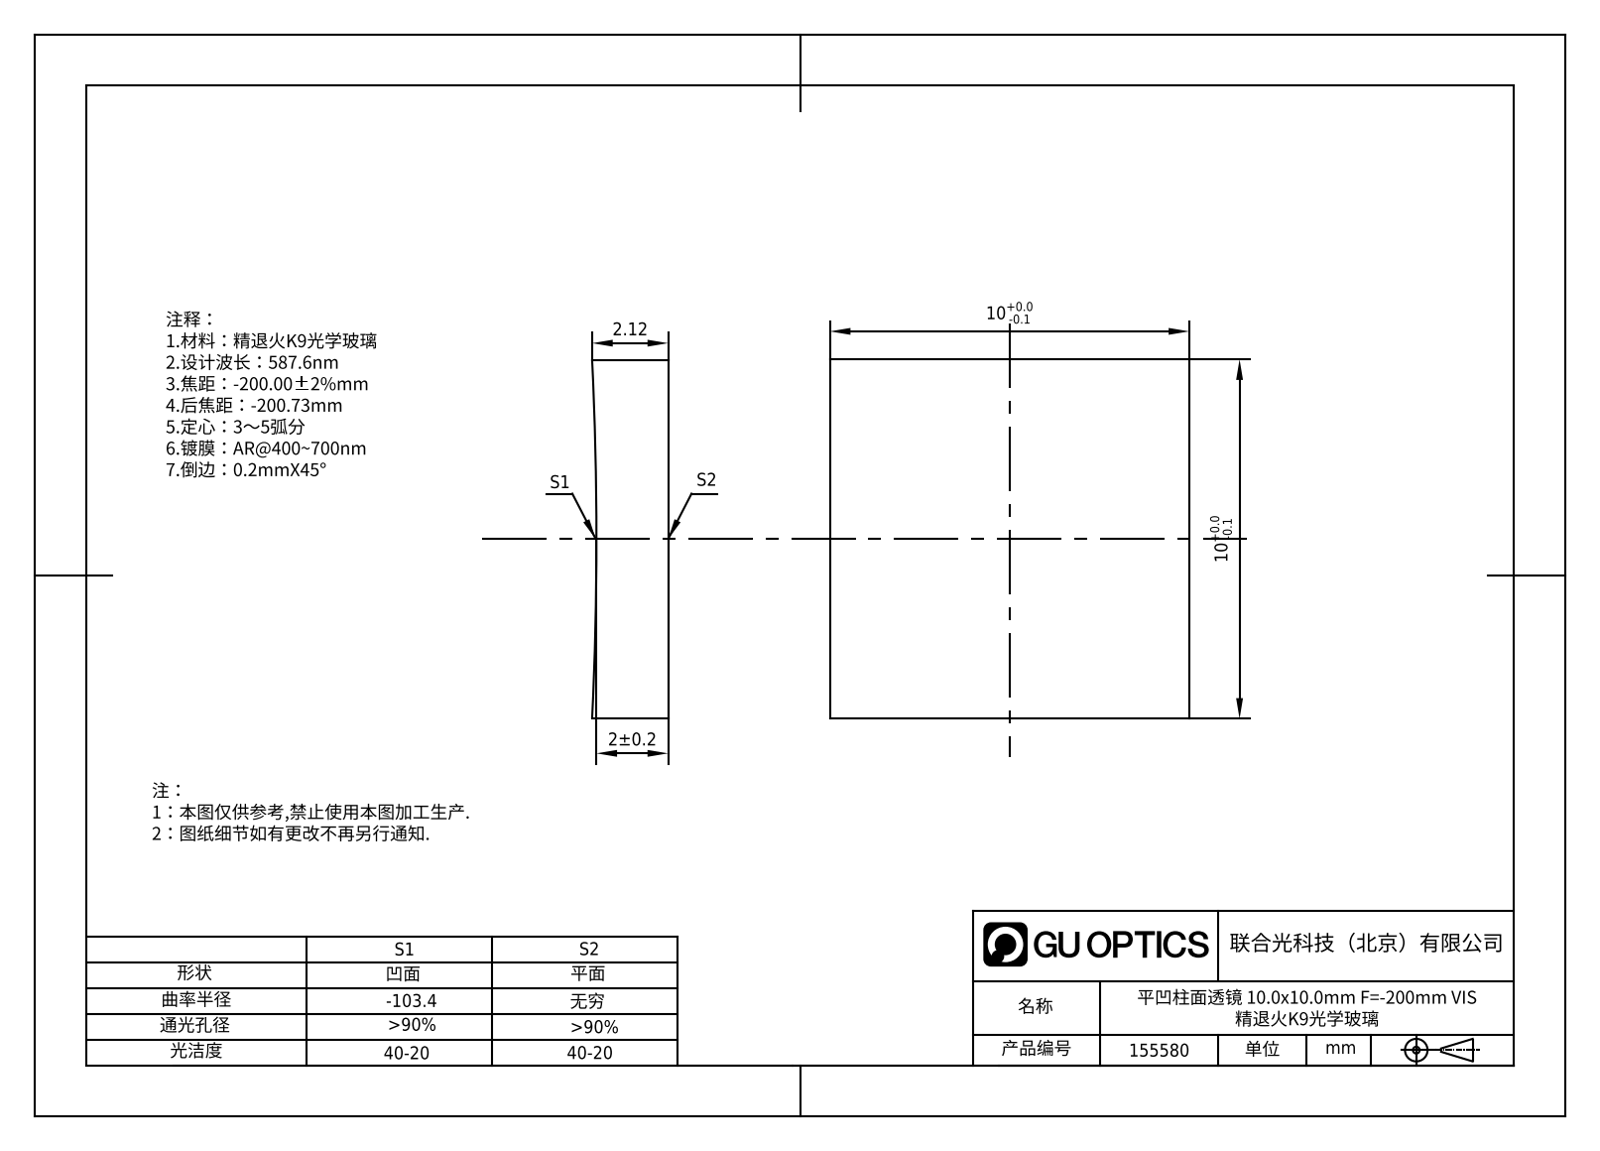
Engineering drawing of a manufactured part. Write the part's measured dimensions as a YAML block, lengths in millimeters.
part_name: "155570"
step_written_by: "SolidWorks 2020 (CONFIG_CONTROL_DESIGN)"
units: millimeters
bodies: {solids: 1, faces: 6, planar: 5, cylindrical: 1, other: 0}
overall_size: [10, 10, 2.12]
volume: 204
surface_area: 283
partial_cylinders:
  - {radius: 103.4, count: 1}
face_to_face_distances: [10]
